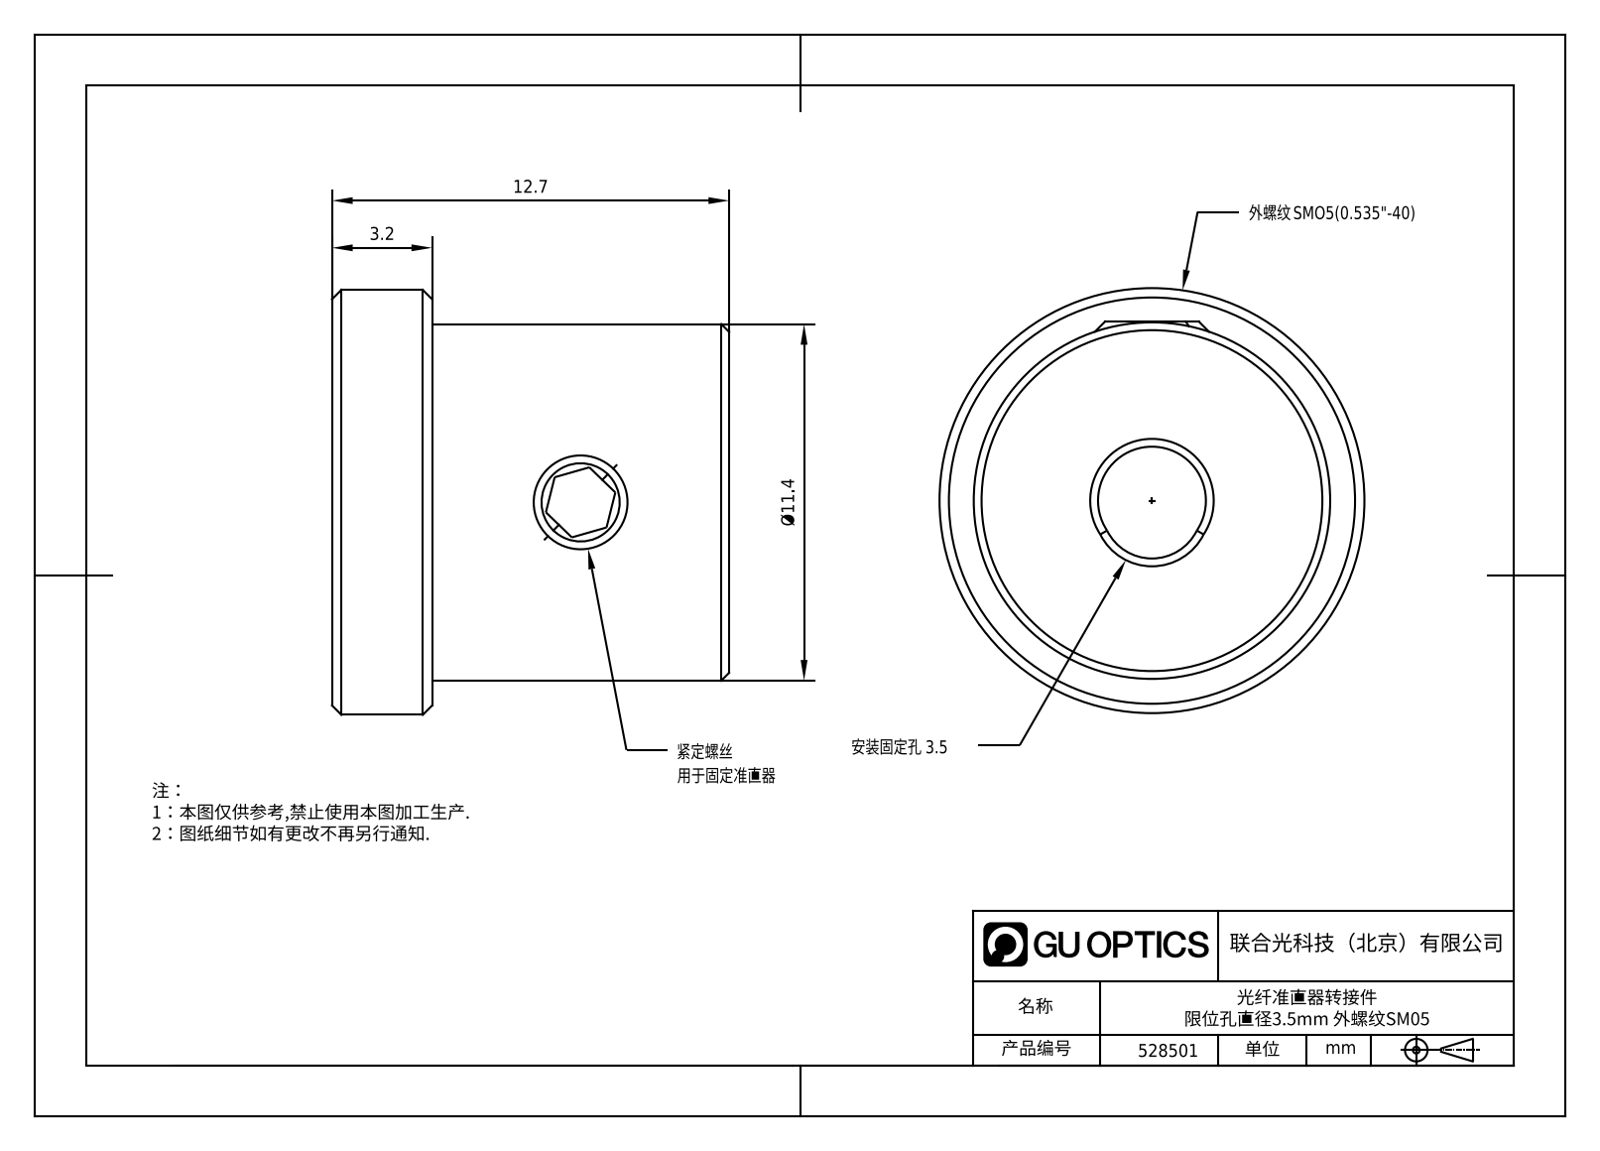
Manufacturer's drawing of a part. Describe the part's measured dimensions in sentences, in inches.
The part is named "30.8.8-14，M4尼龙头顶丝，A_30.8.56-LNJ4*3". Its 3-D file was written by "SolidWorks 2021 (CONFIG_CONTROL_DESIGN)". It is 2 solids with 54 faces: 14 planar, 18 cylindrical and 22 other. Overall it measures 0.535 by 0.535 by 0.5 inches. Its volume is 0.081 cubic inches and its surface area 1.5 square inches. Round holes: 2 of diameter 0.05, 1 of diameter 0.098. Round bosses or shafts: 1 of diameter 0.535, 1 of diameter 0.449, 1 of diameter 0.157, 1 of diameter 0.118. Partial cylindrical surfaces (rounded edges, fillets, slot ends): 1 of radius 0.063, 1 of radius 0.068. The main face-to-face distances are 0.5, 0.126, 0.374, 0.118, 0.079, 0.05, 0.076, 0.45, 0.157, 0.039. The hole center spacings are 0.433.
